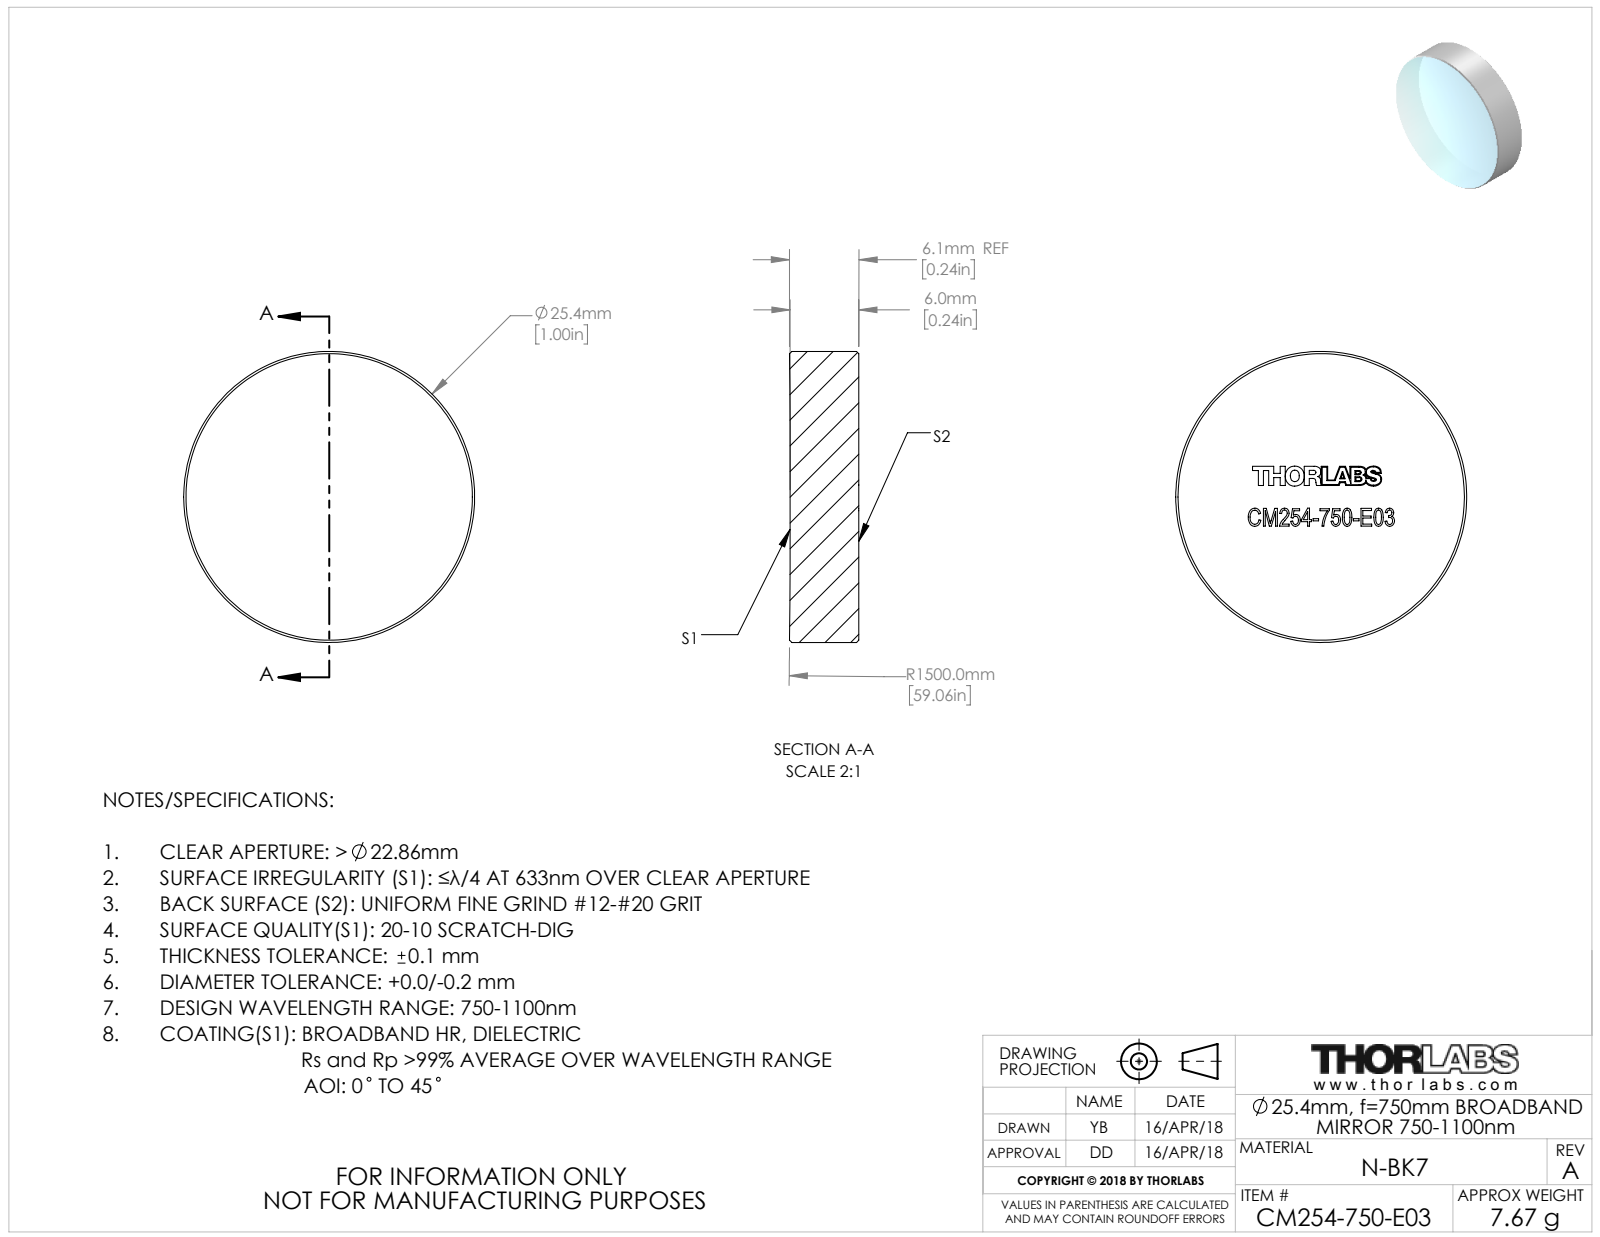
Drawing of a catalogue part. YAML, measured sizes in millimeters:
part_name: "TTN153312-E0W"
step_written_by: "SolidWorks 2018 (CONFIG_CONTROL_DESIGN)"
units: millimeters
bodies: {solids: 1, faces: 40, planar: 32, cylindrical: 2, other: 6}
overall_size: [25.4, 25.4, 6.05]
volume: 3051
surface_area: 1478
round_bosses_or_shafts:
  - {diameter: 25.4, count: 1}
